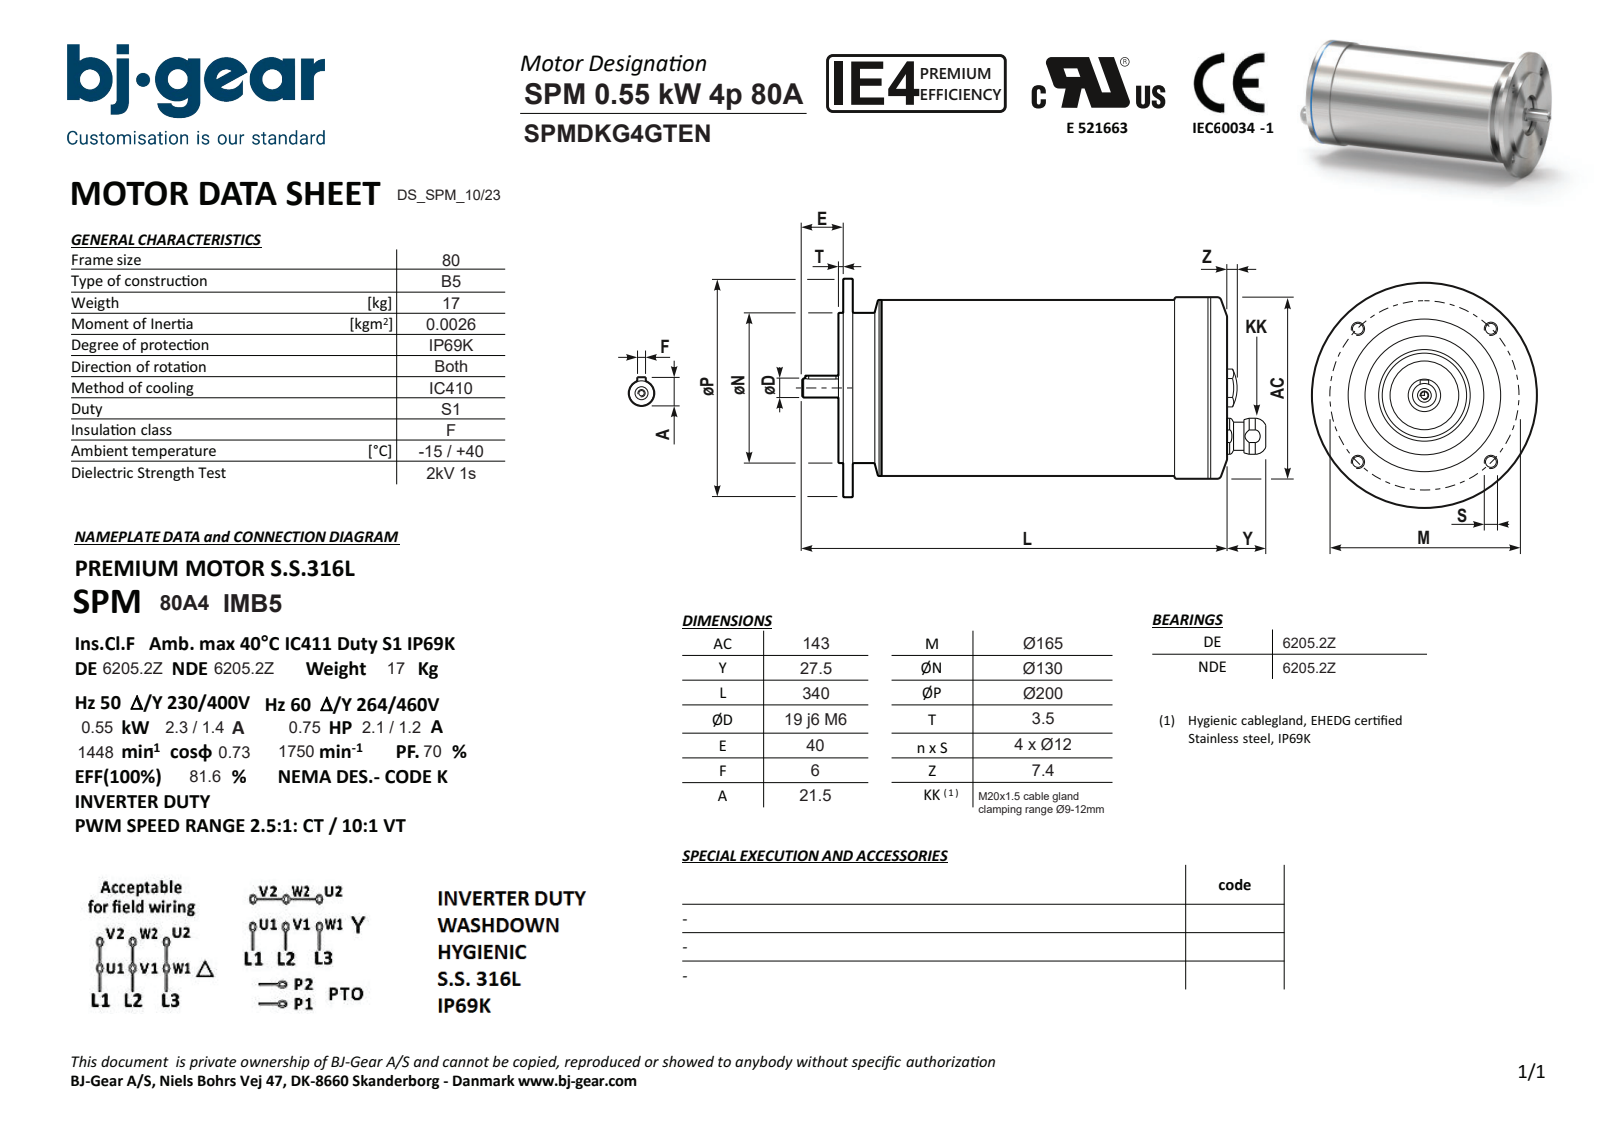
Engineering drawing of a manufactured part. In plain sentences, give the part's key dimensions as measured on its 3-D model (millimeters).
The part is named "SPMDKG4GTENN4KSA1-N---NNN". Its 3-D file was written by "Solid Edge (AUTOMOTIVE_DESIGN)". It is 1 solid with 79 faces: 30 planar, 28 cylindrical and 21 other. Overall it measures 367.5 by 200 by 200 millimeters. Its volume is 4 736 000 cubic millimeters and its surface area 203 697 square millimeters. Round holes: 4 of diameter 12, 1 of diameter 4.92, 1 of diameter 6.4, 1 of diameter 7, 1 of diameter 13.4, 1 of diameter 68. Round bosses or shafts: 1 of diameter 200, 1 of diameter 143, 1 of diameter 142.98, 1 of diameter 139, 1 of diameter 138.98, 1 of diameter 130, 1 of diameter 25, 1 of diameter 20. Partial cylindrical surfaces (rounded edges, fillets, slot ends): 2 of radius 3, 1 of radius 12.8. The main face-to-face distances are 8, 11.5, 3.5, 292, 300, 303.5, 6, 2, 294, 9.5. The hole center spacings are 82.51, 116.68, 61.78, 112.63, 165.01, 38.
